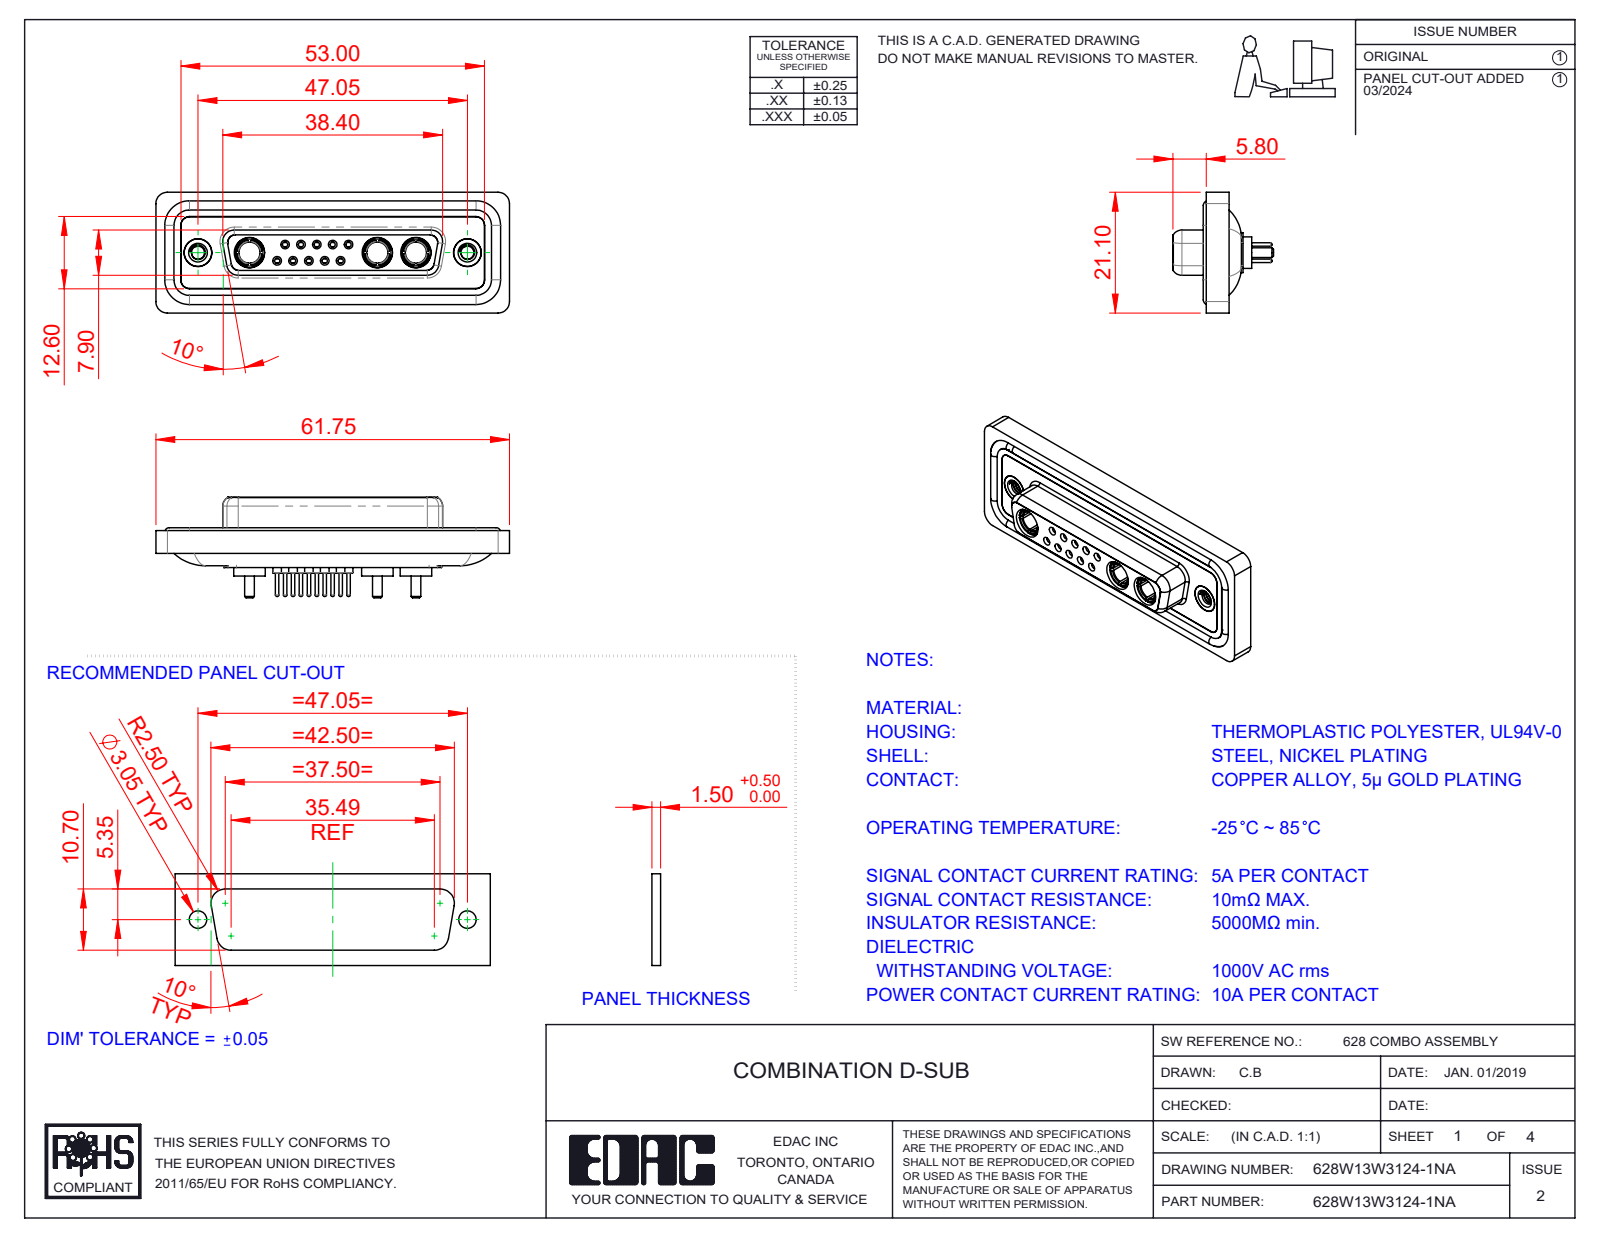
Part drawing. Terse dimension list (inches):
name: 628W13W3124-1NA; 628Combo Housing_13W3; 628Combo Contact Row 1_24; 628Combo Shell Front_25 Contacts (+5 more)
written by: SolidWorks 2023 (CONFIG_CONTROL_DESIGN)
unit: in
bodies: 23 solids, 1156 faces (342 planar, 449 cylindrical, 365 other)
size: 2.431 × 0.831 × 0.691
volume: 0.502 in³; area: 21.19 in²
holes: 10× ⌀0.035, 10× ⌀0.043, 10× ⌀0.059, 10× ⌀0.079, 5× ⌀0.063, 5× ⌀0.067, 5× ⌀0.191, 3× ⌀0.146, 3× ⌀0.209, 2× ⌀0.089, 2× ⌀0.157, 2× ⌀0.159
bosses: 10× ⌀0.087, 10× ⌀0.024, 9× ⌀0.063, 3× ⌀0.217, 3× ⌀0.205, 3× ⌀0.195, 3× ⌀0.187, 3× ⌀0.148
rounds: 22× R0.059, 18× R0.079, 8× R0.053, 8× R0.063, 4× R0.01, 4× R0.02, 4× R0.024, 4× R0.026
face distances: 0.016, 0.071, 0.293, 0.222, 0.02, 0.26, 0.278, 0.063, 0.114, 0.043
hole spacings: 0.124, 0.109, 0.198, 0.198, 0.218, 0.327, 0.295, 0.109
